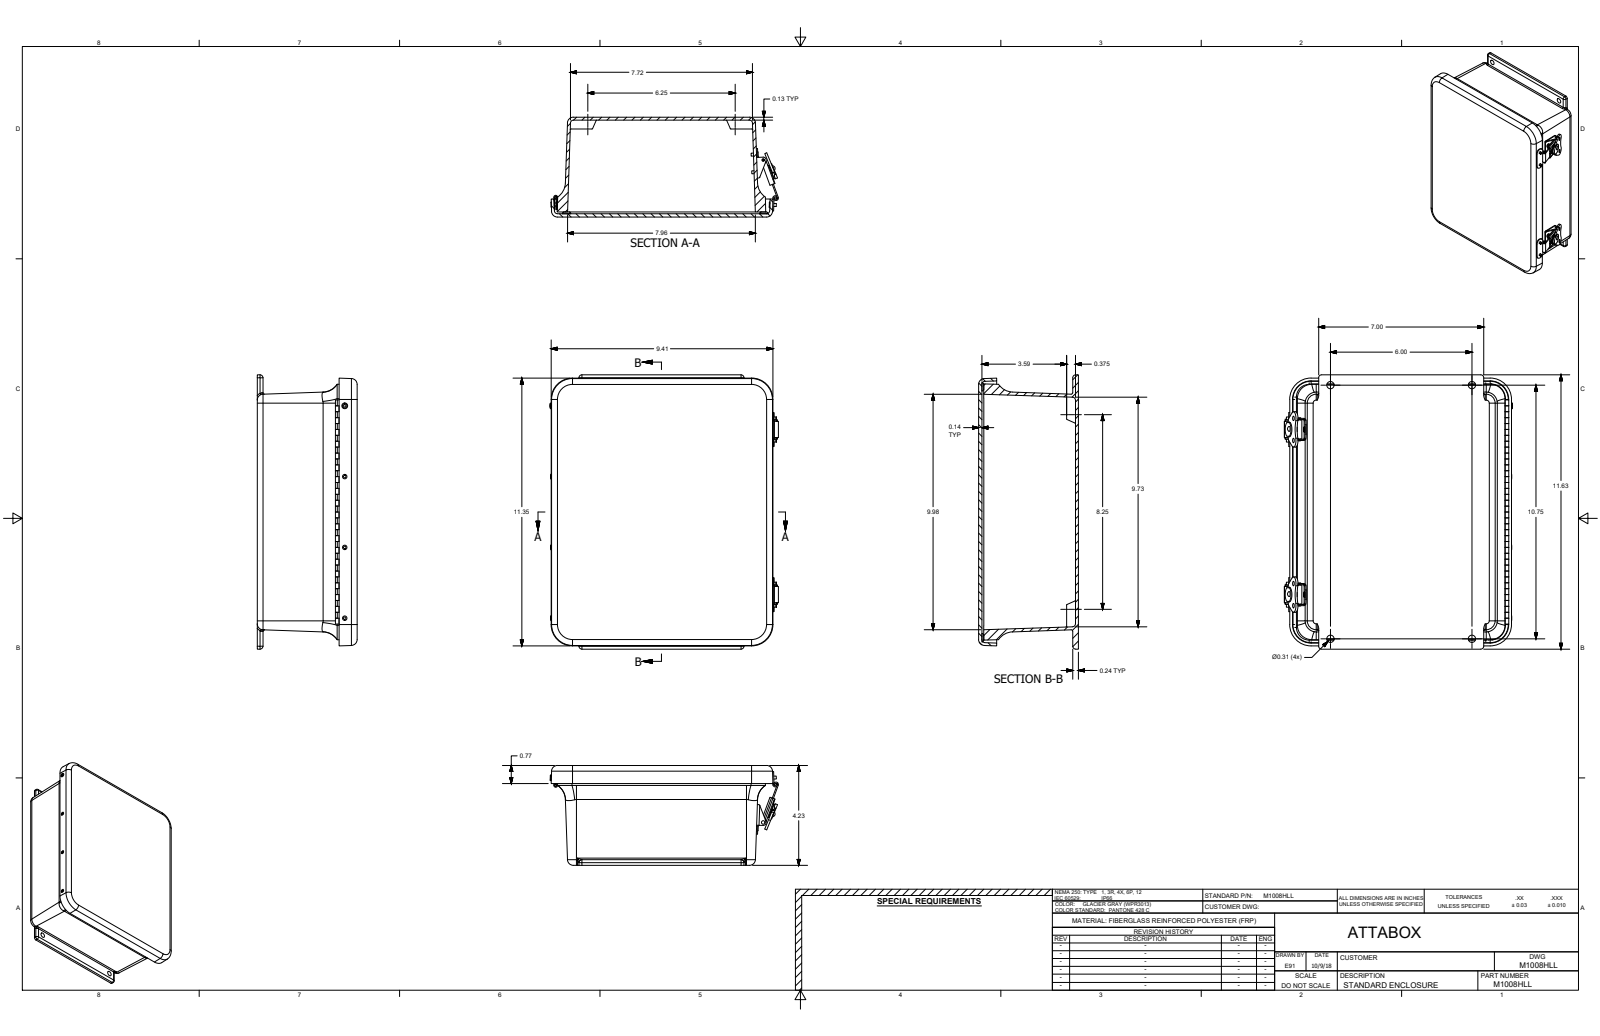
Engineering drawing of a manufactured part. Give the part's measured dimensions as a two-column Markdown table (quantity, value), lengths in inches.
| quantity | value |
| --- | --- |
| part name | M1008HLL |
| STEP written by | SolidWorks 2018 (AUTOMOTIVE_DESIGN) |
| units | inches |
| bodies | 46 solids, 1097 faces (456 planar, 453 cylindrical, 188 other) |
| overall size | 11.63 × 9.676 × 4.234 |
| volume | 60.23 in³ |
| surface area | 835.8 in² |
| round holes (diameter × count) | 0.14 × 18, 0.104 × 16, 0.131 × 8, 0.152 × 8, 0.13 × 4, 0.133 × 4, 0.159 × 4, 0.187 × 4, 0.218 × 4, 0.312 × 4, 0.135 × 2, 0.189 × 2 |
| round bosses / shafts (diameter × count) | 0.125 × 14, 0.27 × 4, 0.125 × 4, 0.66 × 2, 0.582 × 2, 0.525 × 2, 0.286 × 2, 0.213 × 2 |
| partial cylindrical surfaces (radius × count) | 0.031 × 36, 0.125 × 17, 0.015 × 16, 0.06 × 13, 0.25 × 10, 0.011 × 8, 0.02 × 8, 0.055 × 8 |
| main face-to-face distances | 0.142, 4.092, 4.233, 0.125, 3.967, 4.109, 0.12, 0.077, 3.89, 4.015 |
| hole center spacings | 6, 7, 3, 2.5, 0.125, 0.725, 0.75, 1.337 |
